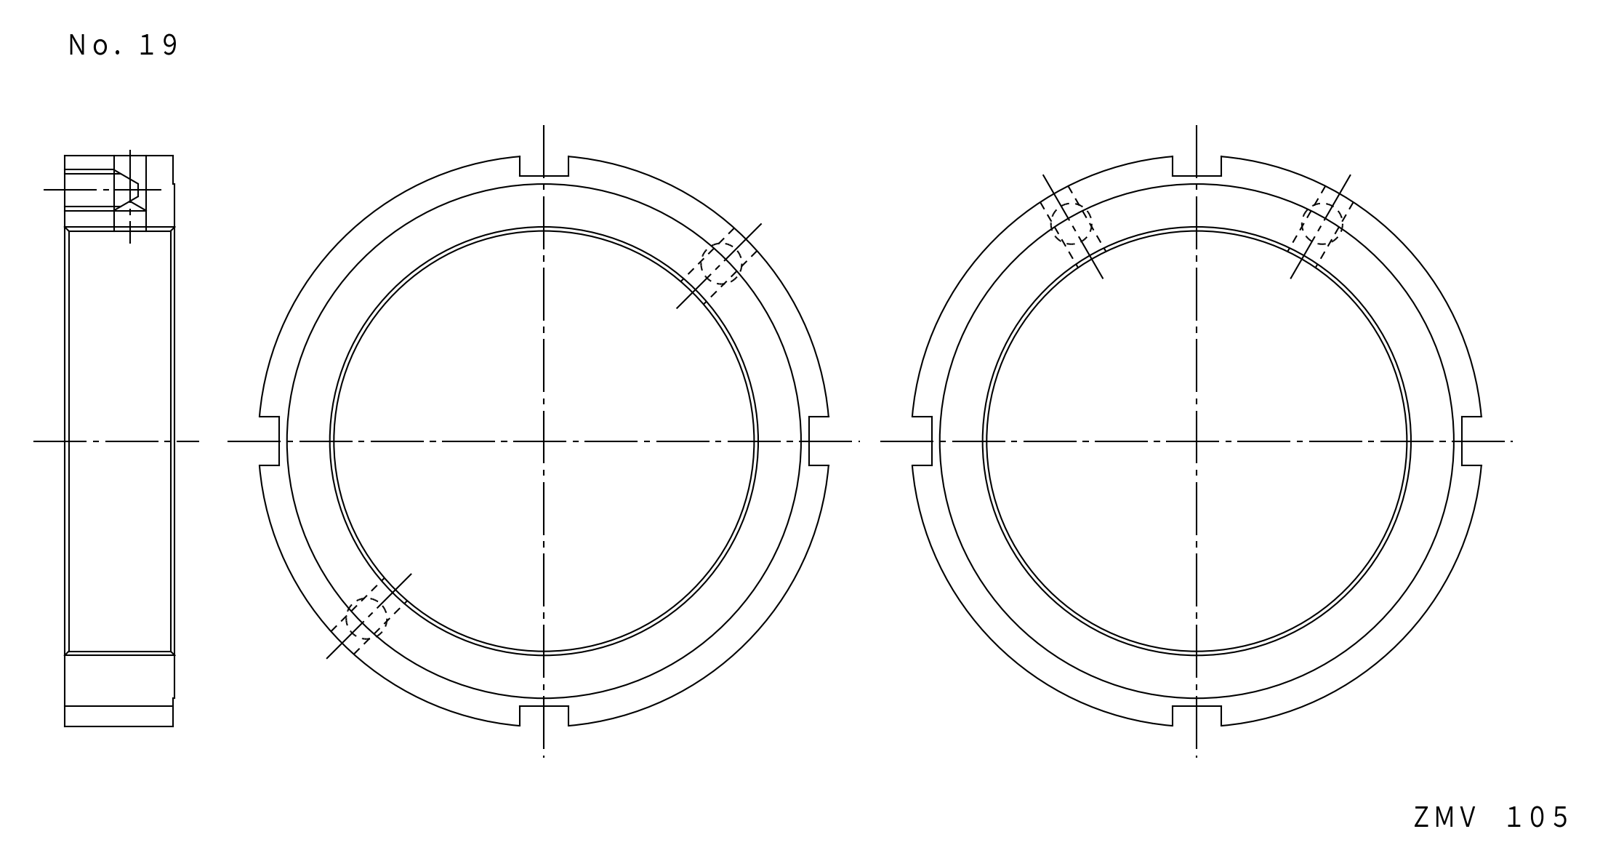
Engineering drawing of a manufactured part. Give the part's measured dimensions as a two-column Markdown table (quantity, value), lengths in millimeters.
| quantity | value |
| --- | --- |
| part name | FKD ZMV105 |
| STEP written by | Autodesk Inventor LT (CONFIG_CONTROL_DESIGN) |
| units | millimeters |
| bodies | 1 solid, 29 faces (15 planar, 10 cylindrical, 4 other) |
| overall size | 139.49 × 139.49 × 27 |
| volume | 171 004 mm³ |
| surface area | 35 903 mm² |
| round holes (diameter × count) | 7.9 × 2, 8.38 × 2, 105 × 1 |
| round bosses / shafts (diameter × count) | 140 × 1, 126 × 1 |
| main face-to-face distances | 27, 0.5, 26.5, 59, 71, 130, 12 |
| hole center spacings | 61.5, 123.01 |
